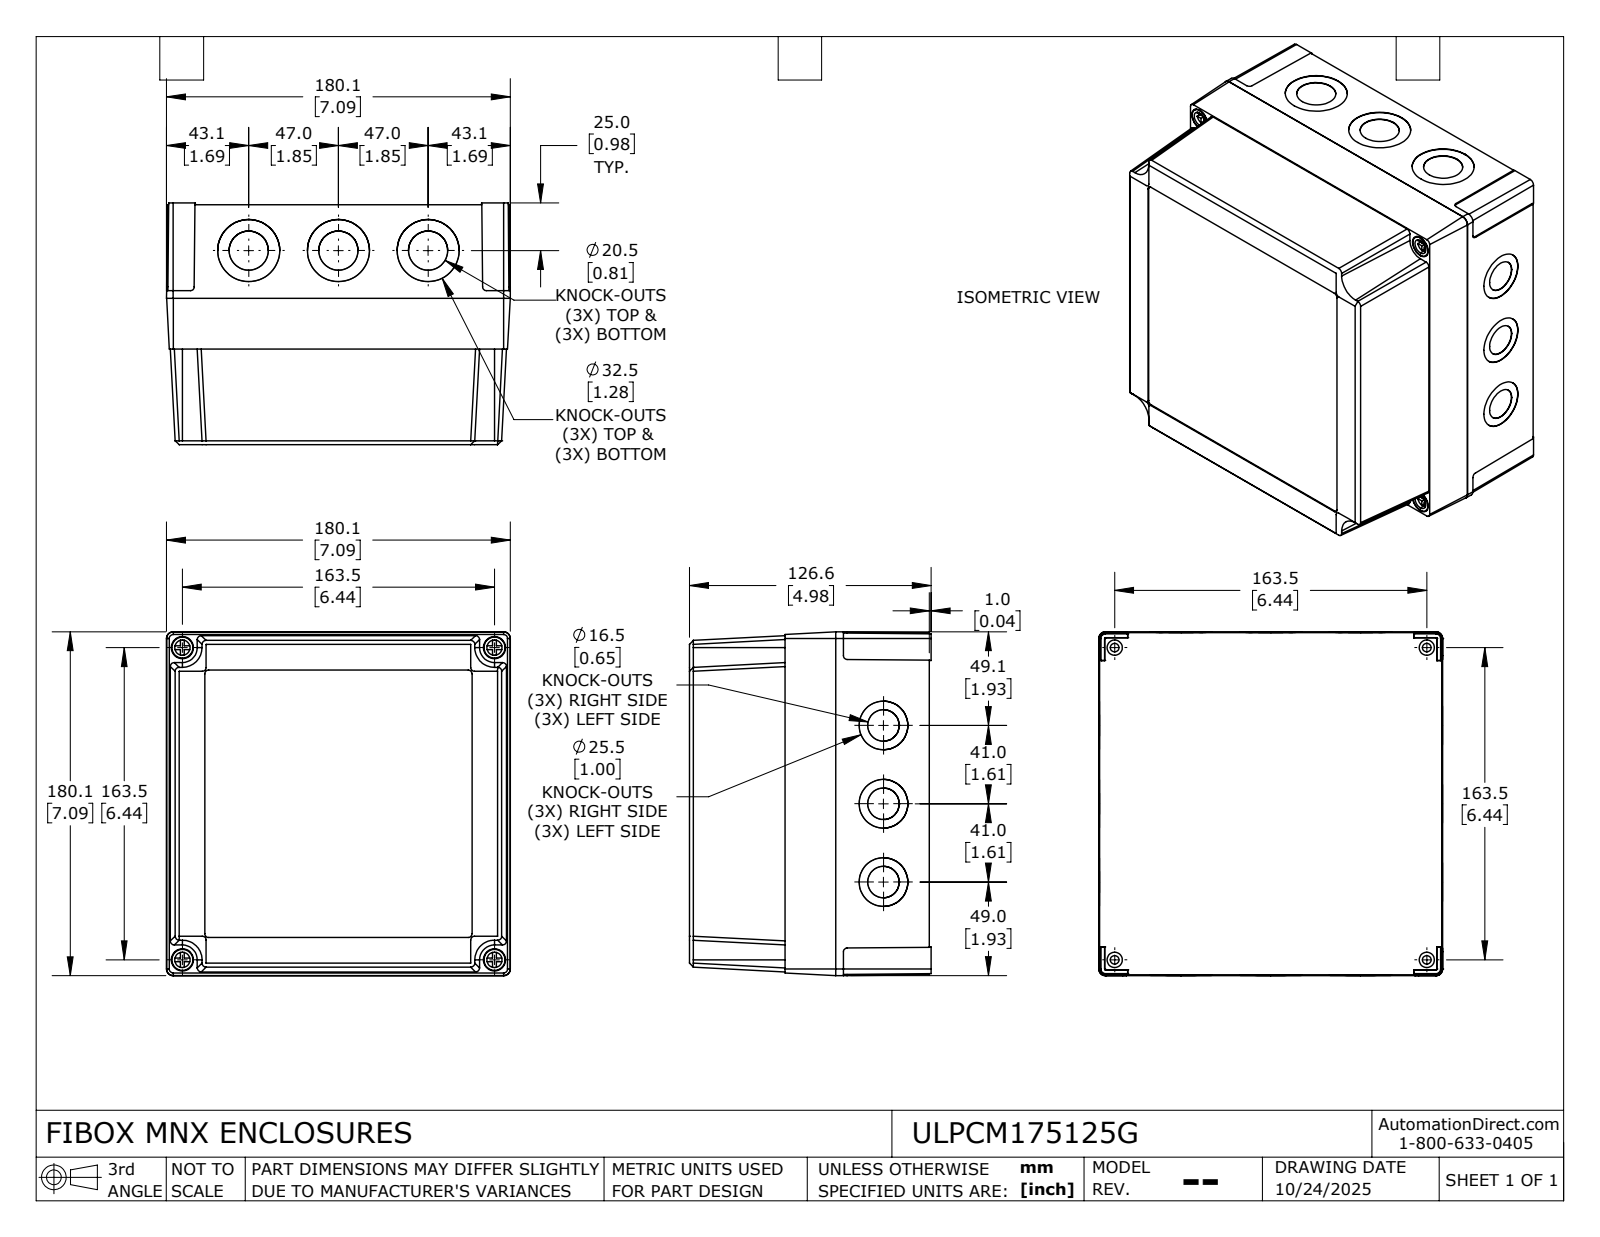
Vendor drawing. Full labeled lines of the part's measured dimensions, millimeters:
Part name (STEP PRODUCT): ULPCM175125G_Default
STEP written by: SolidWorks 2024 (CONFIG_CONTROL_DESIGN)
Units: millimetres
Bodies: 6 solids, 629 faces (351 planar, 232 cylindrical, 46 other)
Overall size (bounding box): 180.1 × 180.1 × 126.6
Volume: 442 000 mm³ · Surface area: 309 500 mm²
Round holes (diameter × count): ⌀3.2 ×12, ⌀4 ×12, ⌀16.5 ×6, ⌀20.5 ×6, ⌀25.5 ×6, ⌀32.5 ×6, ⌀4.5 ×4, ⌀8 ×4, ⌀11.6 ×4
Round bosses / shafts (diameter × count): ⌀8 ×12, ⌀2.5 ×8, ⌀11 ×4, ⌀7.2 ×4
Partial cylindrical surfaces — rounded edges, fillets, slot ends (radius × count): R2 ×8, R2.1 ×8, R2.8 ×6, R1.1 ×4, R5 ×4, R1.2 ×2
Main face-to-face distances: 3, 122.6, 119.6, 1.4, 4.2, 2.5, 125.1, 122.1, 2, 0.6
Hole centre spacings: 33.9, 50, 72.8, 82.6, 121.7, 132.3, 138.9, 148.7
